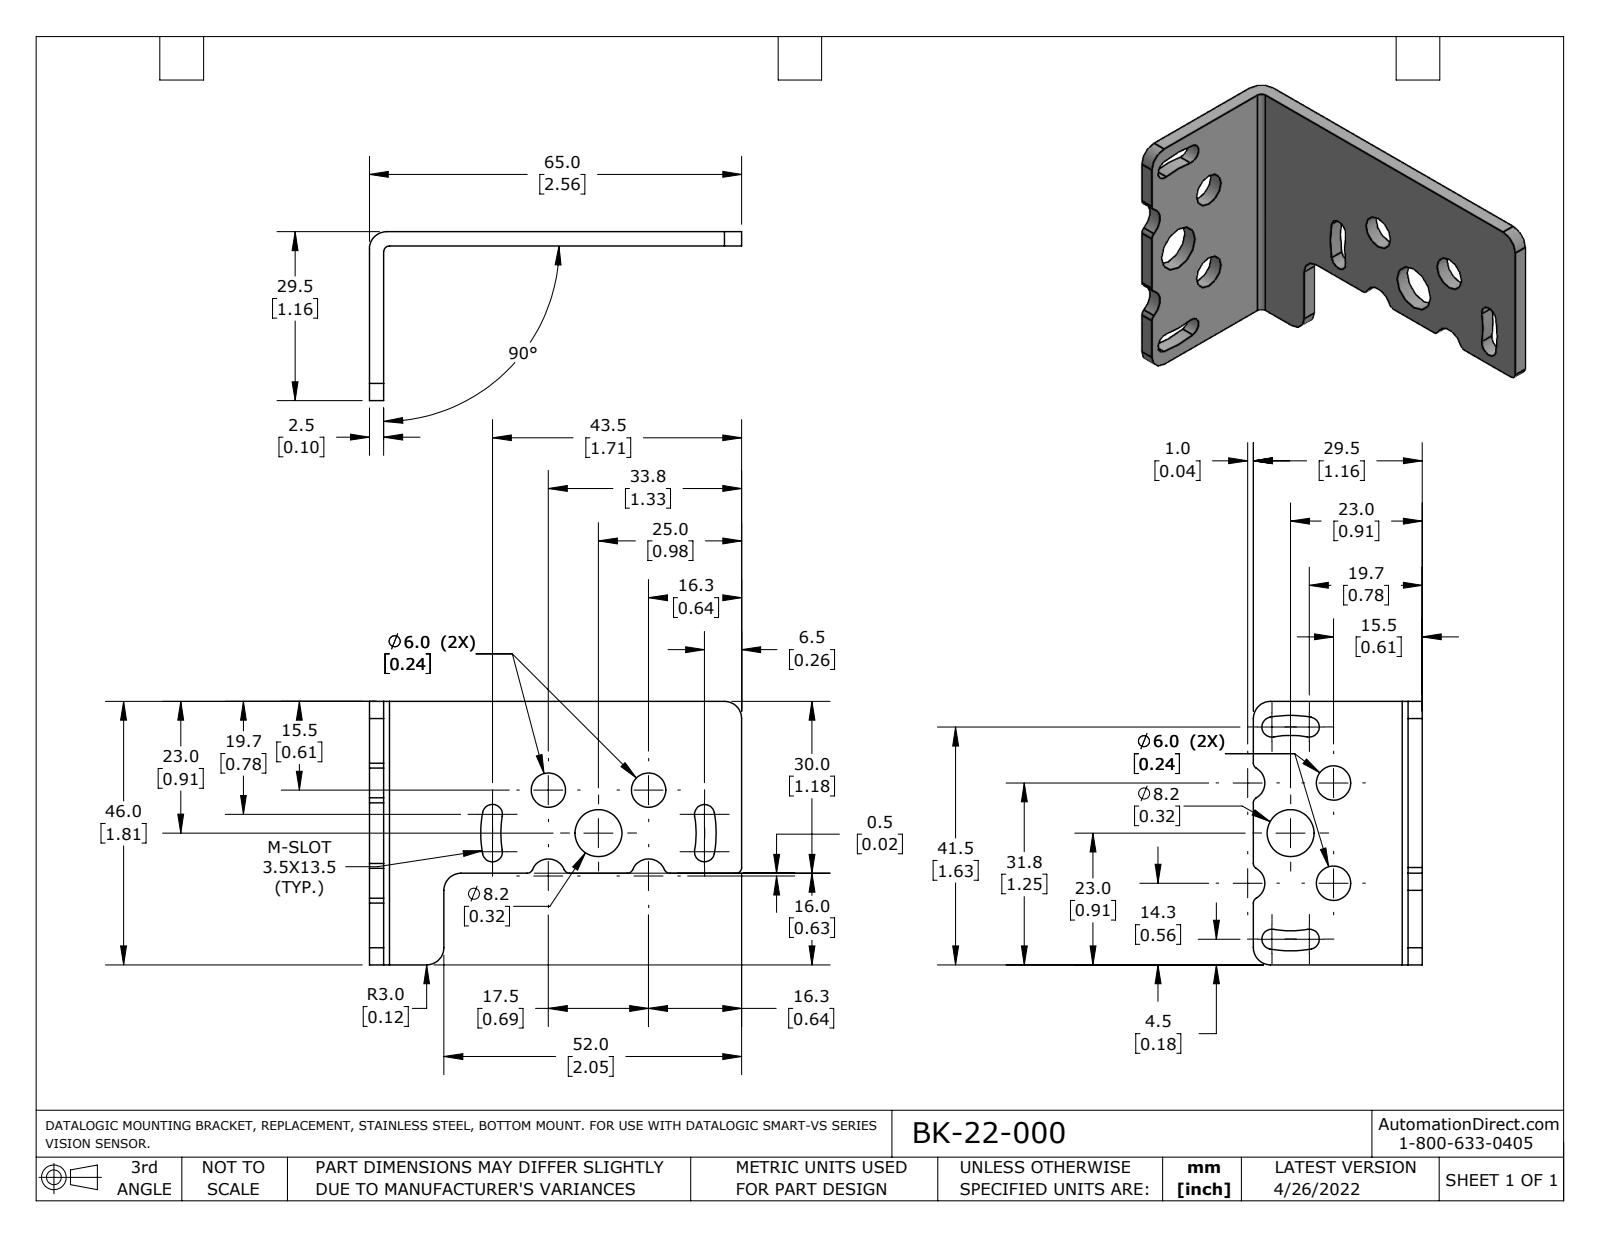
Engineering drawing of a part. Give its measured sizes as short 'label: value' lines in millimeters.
name: BK-22-000
written by: SolidWorks 2021 (AUTOMOTIVE_DESIGN)
unit: mm
bodies: 1 solid, 56 faces (14 planar, 39 cylindrical, 3 other)
size: 65 × 46 × 29.5
volume: 7 440 mm³; area: 7 181 mm²
holes: 4× ⌀6, 2× ⌀8.2
rounds: 10× R1, 10× R3, 5× R1.8, 2× R17, 2× R20.5
face distances: 2.5, 46, 16, 30, 29.5, 27, 65, 62.5, 13, 10.5
hole spacings: 11.5, 17.5
